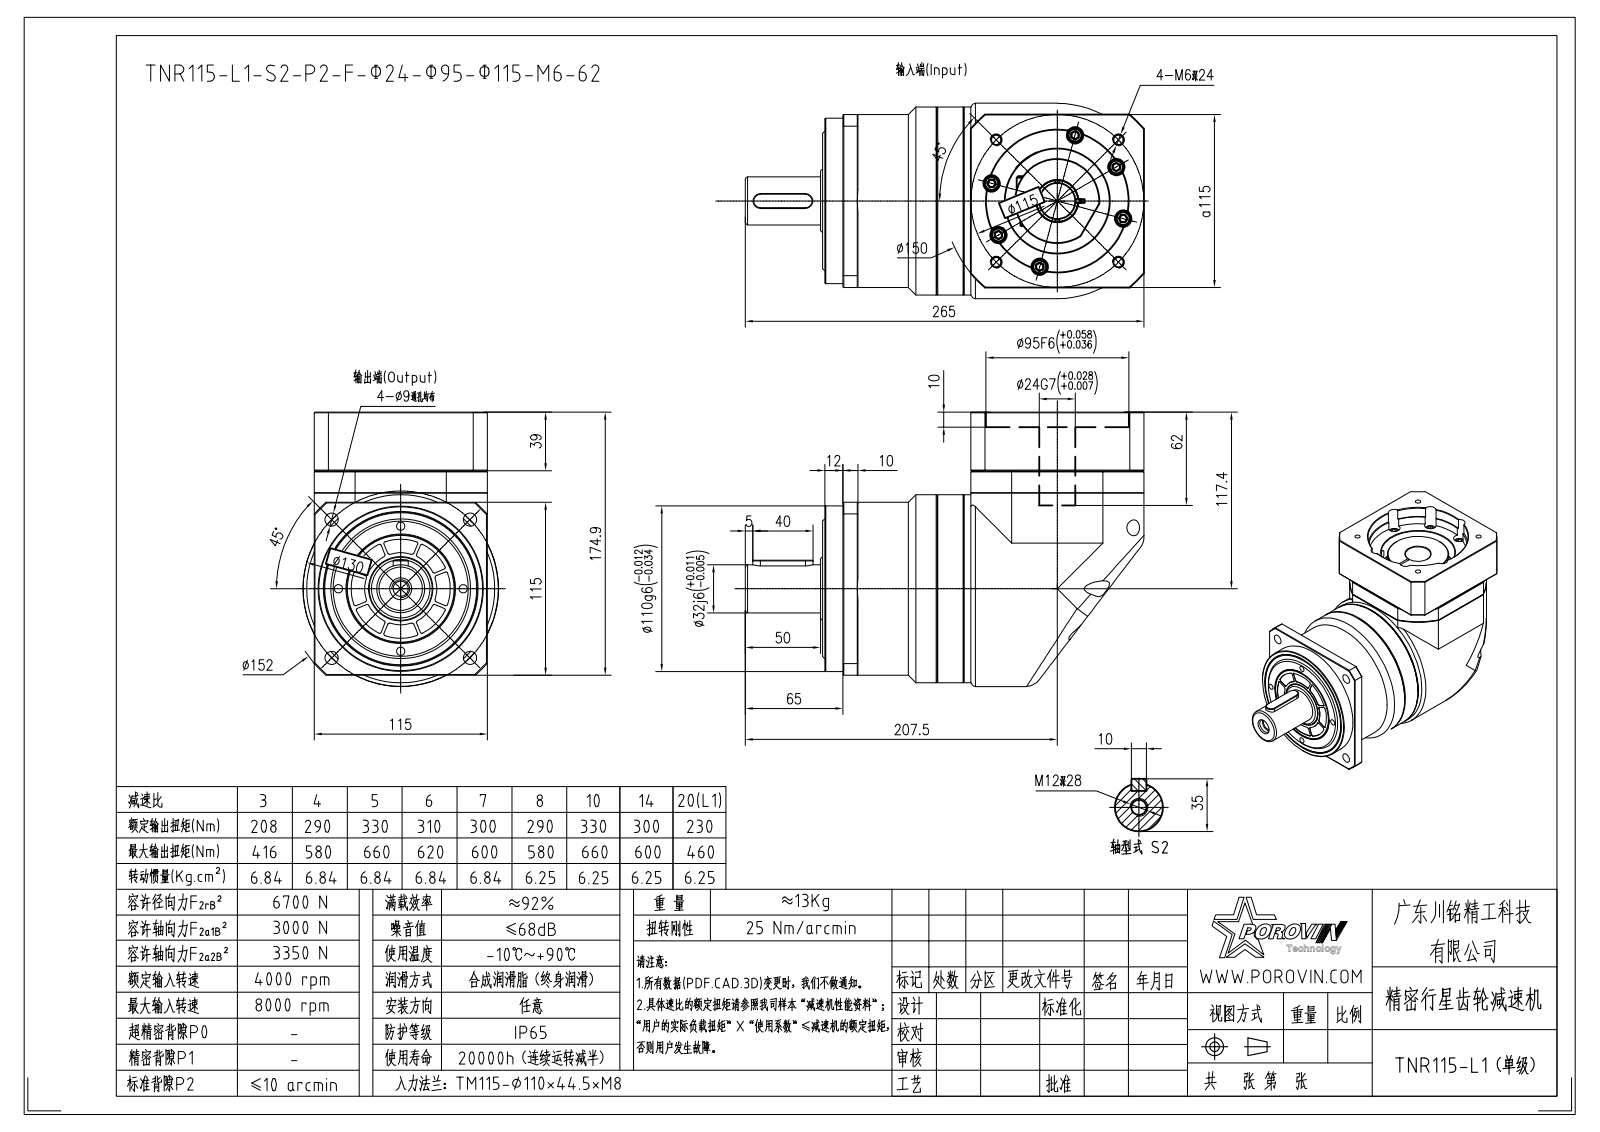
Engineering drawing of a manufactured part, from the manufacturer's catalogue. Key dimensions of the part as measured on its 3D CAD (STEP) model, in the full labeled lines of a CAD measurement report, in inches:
Part name (STEP PRODUCT): HEXAGON_SOCKET_HEAD_CAP_SC-7135; SPRING_LOCK_WASHERS--NORMAL_TYP; TNR1150003; 65X55X700 (+8 more)
STEP written by: CREO PARAMETRIC BY PTC INC, 2020053 (CONFIG_CONTROL_DESIGN)
Units: inches
Bodies: 50 solids, 1401 faces (580 planar, 566 cylindrical, 255 other)
Overall size (bounding box): 10.433 × 7.181 × 5.118
Volume: 171.9 in³ · Surface area: 528.5 in²
Round holes (diameter × count): ⌀0.263 ×19, ⌀0.256 ×13, ⌀0.197 ×12, ⌀0.433 ×12, ⌀0.413 ×7, ⌀0.26 ×6, ⌀0.217 ×4, ⌀0.354 ×4, ⌀2.835 ×2, ⌀0.268 ×1, ⌀0.335 ×1, ⌀0.402 ×1
Round bosses / shafts (diameter × count): ⌀0.394 ×19, ⌀0.389 ×19, ⌀0.236 ×19, ⌀5.118 ×1, ⌀4.921 ×1, ⌀4.882 ×1, ⌀4.528 ×1, ⌀4.331 ×1
Partial cylindrical surfaces — rounded edges, fillets, slot ends (radius × count): R0.039 ×64, R0.197 ×3, R0.266 ×1, R0.394 ×1, R1.831 ×1, R1.87 ×1, R2.559 ×1, R2.953 ×1
Main face-to-face distances: 0.709, 0.701, 4.528, 0.587, 2.122, 5.413, 4.713, 4.705, 0.177, 0.134
Hole centre spacings: 1.781, 2.254, 1.623, 1.818, 3.822, 3.89, 3.62, 1.828
